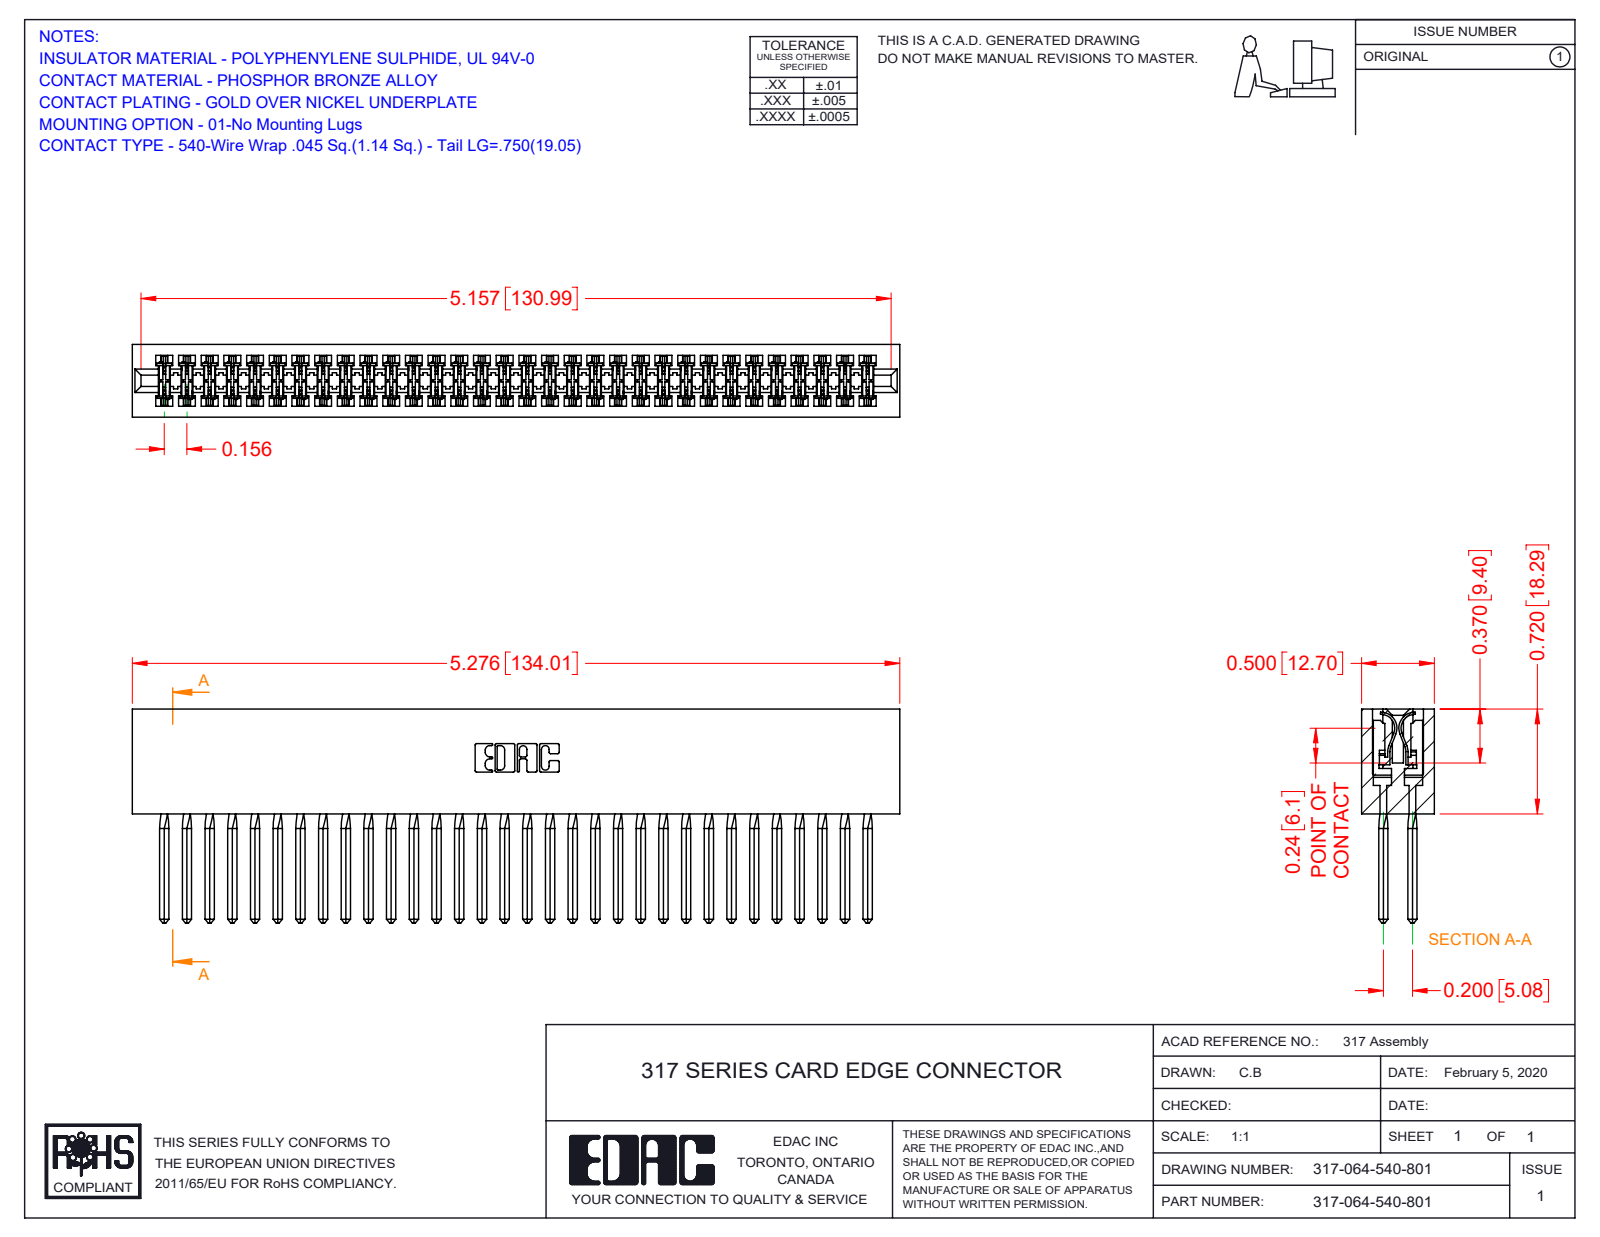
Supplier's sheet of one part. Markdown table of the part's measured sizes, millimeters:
| quantity | value |
| --- | --- |
| part name | 317-064-540-801; 317-290-001_540; 317 Part_Lugless |
| STEP written by | SolidWorks 2016 (CONFIG_CONTROL_DESIGN) |
| units | millimeters |
| bodies | 65 solids, 5786 faces (4722 planar, 808 cylindrical, 256 other) |
| overall size | 134 × 37.3 × 12.7 |
| volume | 23 940 mm³ |
| surface area | 35 580 mm² |
| partial cylindrical surfaces (radius × count) | 0.4 × 128, 0.3 × 22, 0.2 × 6, 0.8 × 6, 0.7 × 3, 2.4 × 2, 2.5 × 2, 2.8 × 2 |
| main face-to-face distances | 1.9, 12.7, 10.8, 8.9, 2.8, 5, 2.4, 5.1, 2.9, 3.3 |
